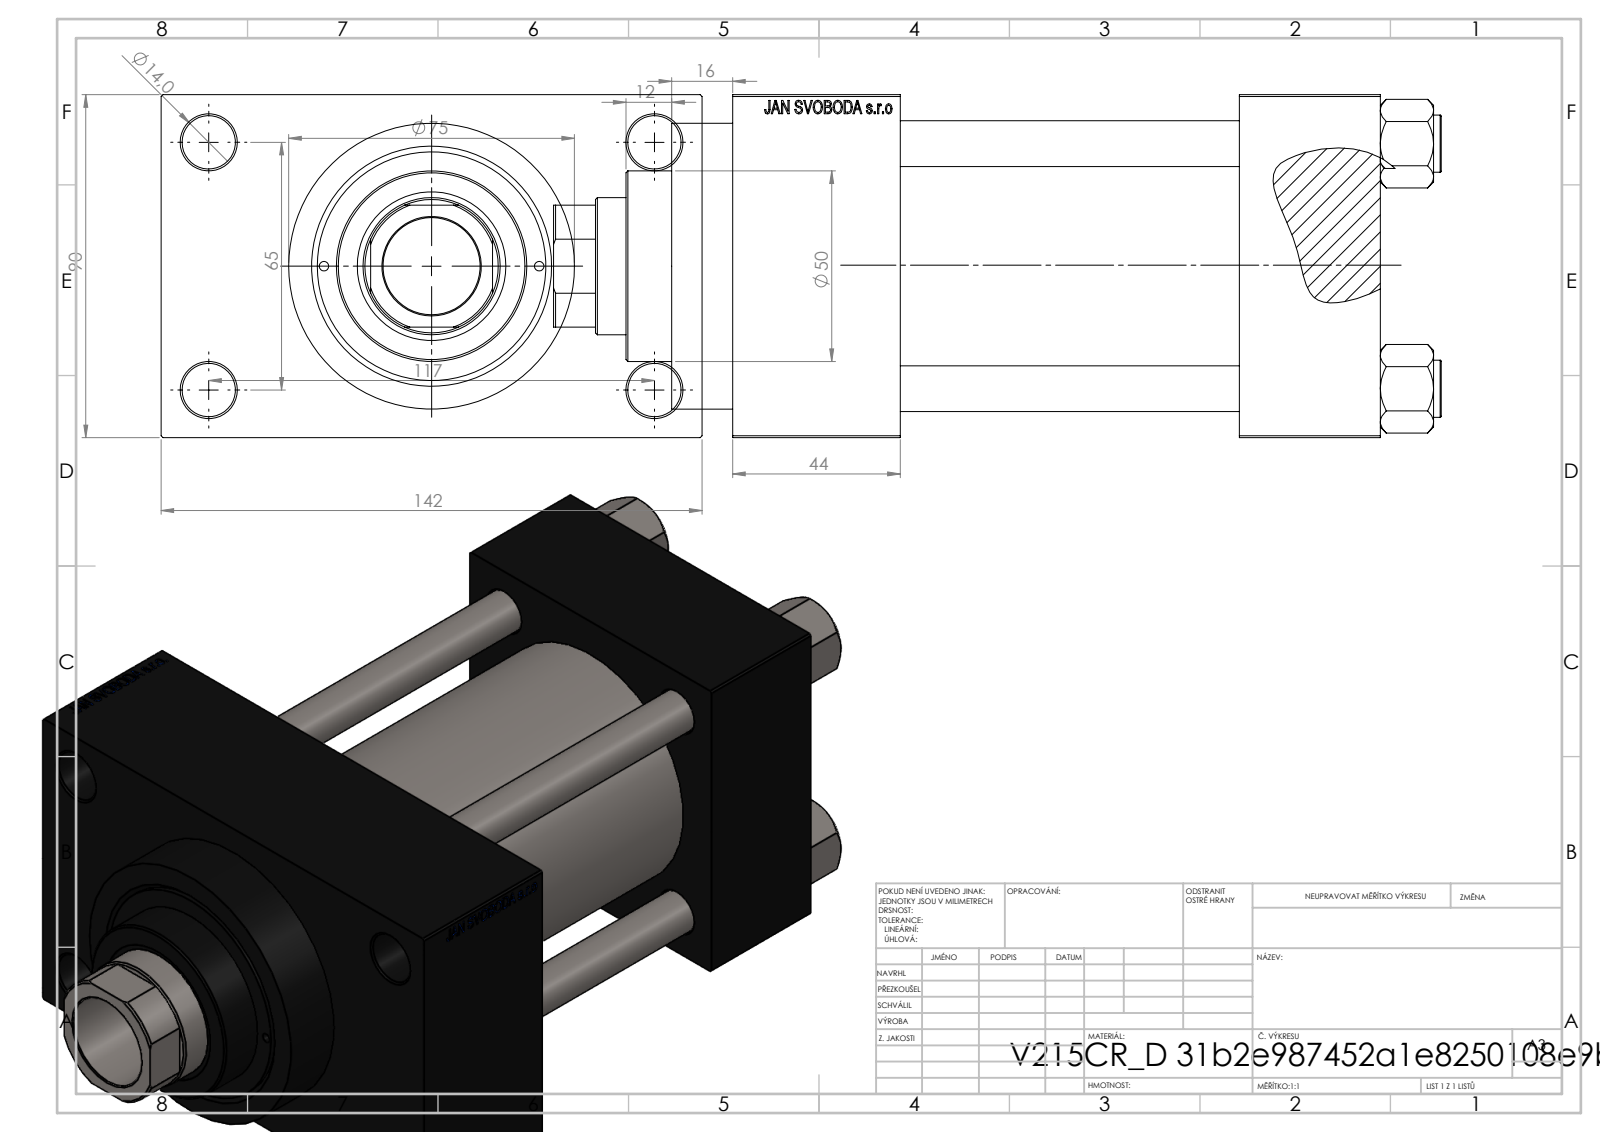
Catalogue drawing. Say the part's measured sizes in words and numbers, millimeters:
The part is named "V215_VC_A; V215CR_D_TYCINKA; V215CR_VCP_D; V215CR_D_Body (+1 more)". Its 3-D file was written by "SolidWorks 2019 (CONFIG_CONTROL_DESIGN)". It is 11 solids with 1111 faces: 499 planar, 92 cylindrical and 520 other. Overall it measures 233 by 142 by 90 millimeters. Its volume is 1 174 000 cubic millimeters and its surface area 226 057 square millimeters. Round holes: 4 of diameter 12, 4 of diameter 14, 2 of diameter 2.5, 2 of diameter 7, 2 of diameter 20.96, 2 of diameter 30, 1 of diameter 25.5, 1 of diameter 36, 1 of diameter 39, 1 of diameter 50, 1 of diameter 60, 1 of diameter 63. Round bosses or shafts: 4 of diameter 15, 1 of diameter 75, 1 of diameter 69. Partial cylindrical surfaces (rounded edges, fillets, slot ends): 1 of radius 17.5. The main face-to-face distances are 90, 89, 37, 126, 170, 133, 44, 26, 116, 142. The hole center spacings are 26.35, 32.39, 44.4, 45.47, 64.3, 66.92, 68.42, 69.81.
